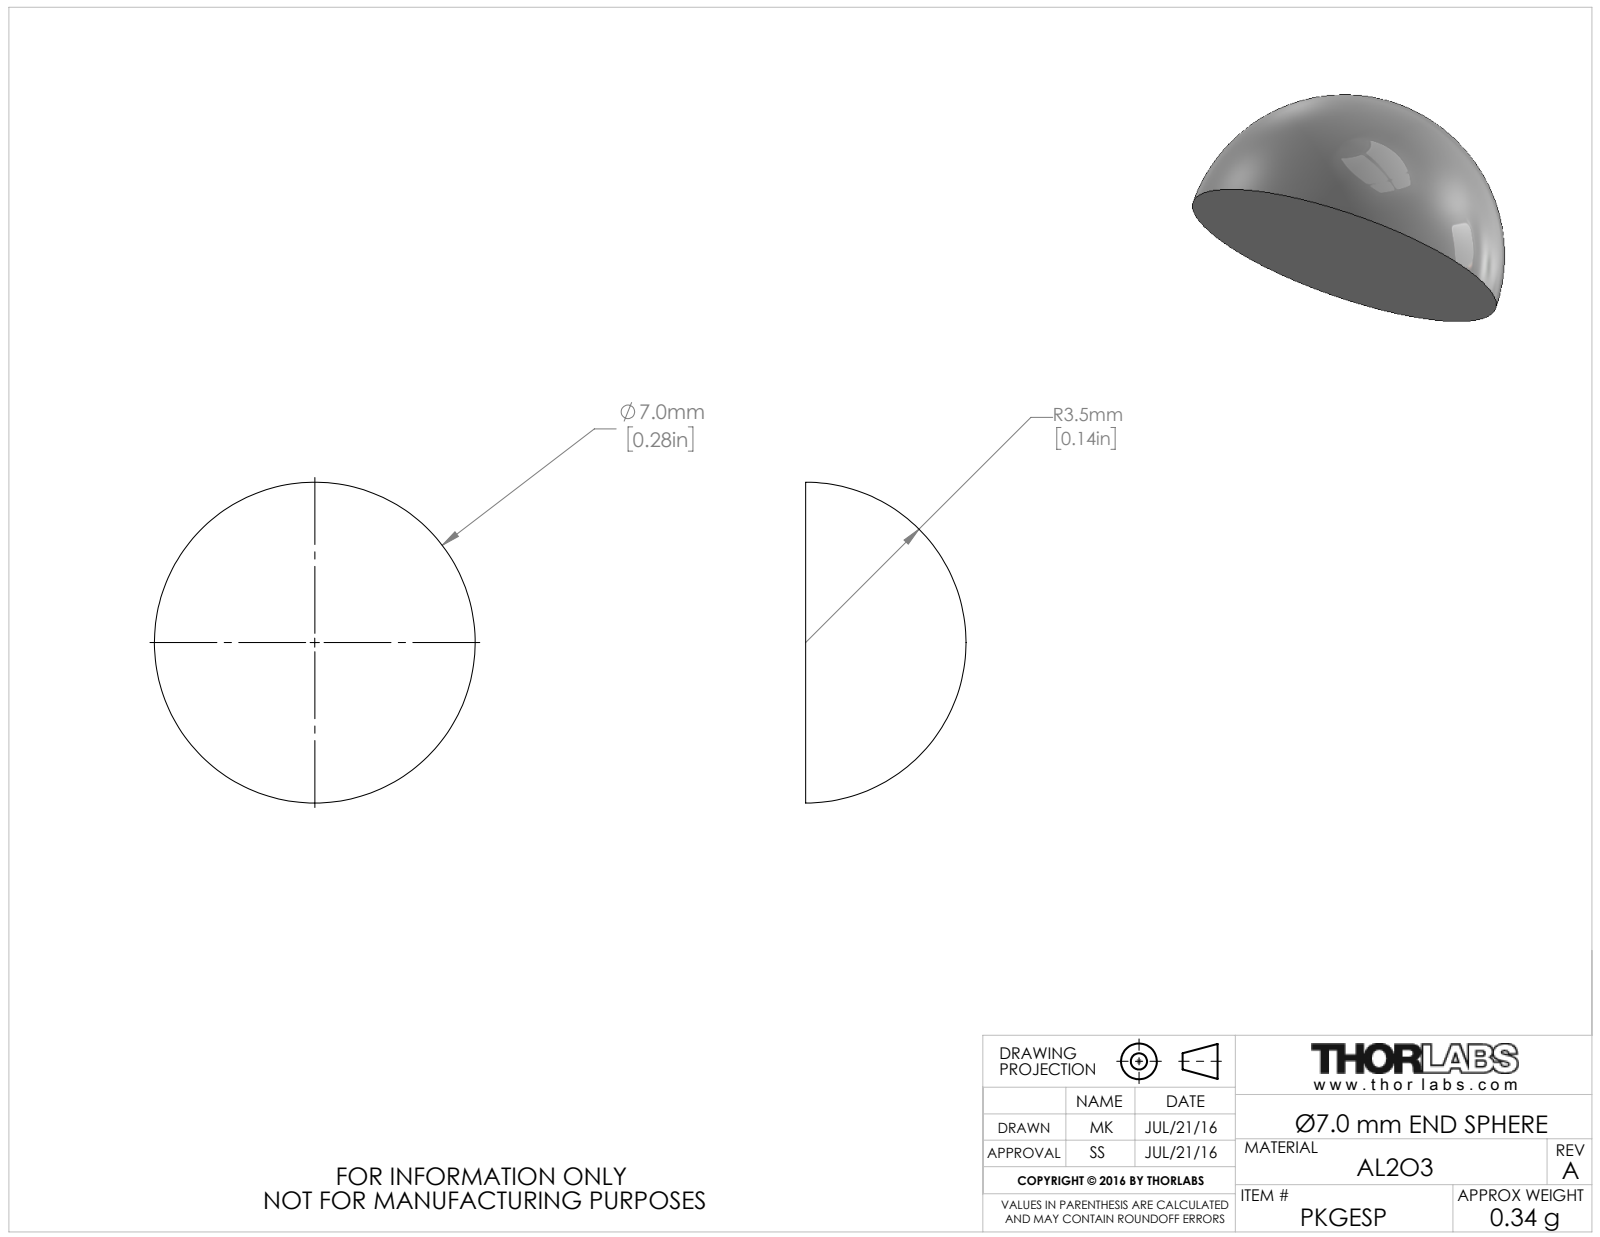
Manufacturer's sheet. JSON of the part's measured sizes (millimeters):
{"part_name": "CTN002731", "step_written_by": "SolidWorks 2016 (AUTOMOTIVE_DESIGN)", "units": "millimeters", "bodies": {"solids": 1, "faces": 3, "planar": 1, "cylindrical": 0, "other": 2}, "overall_size": [7, 7, 3.5], "volume_mm3": 90, "surface_area_mm2": 115}
